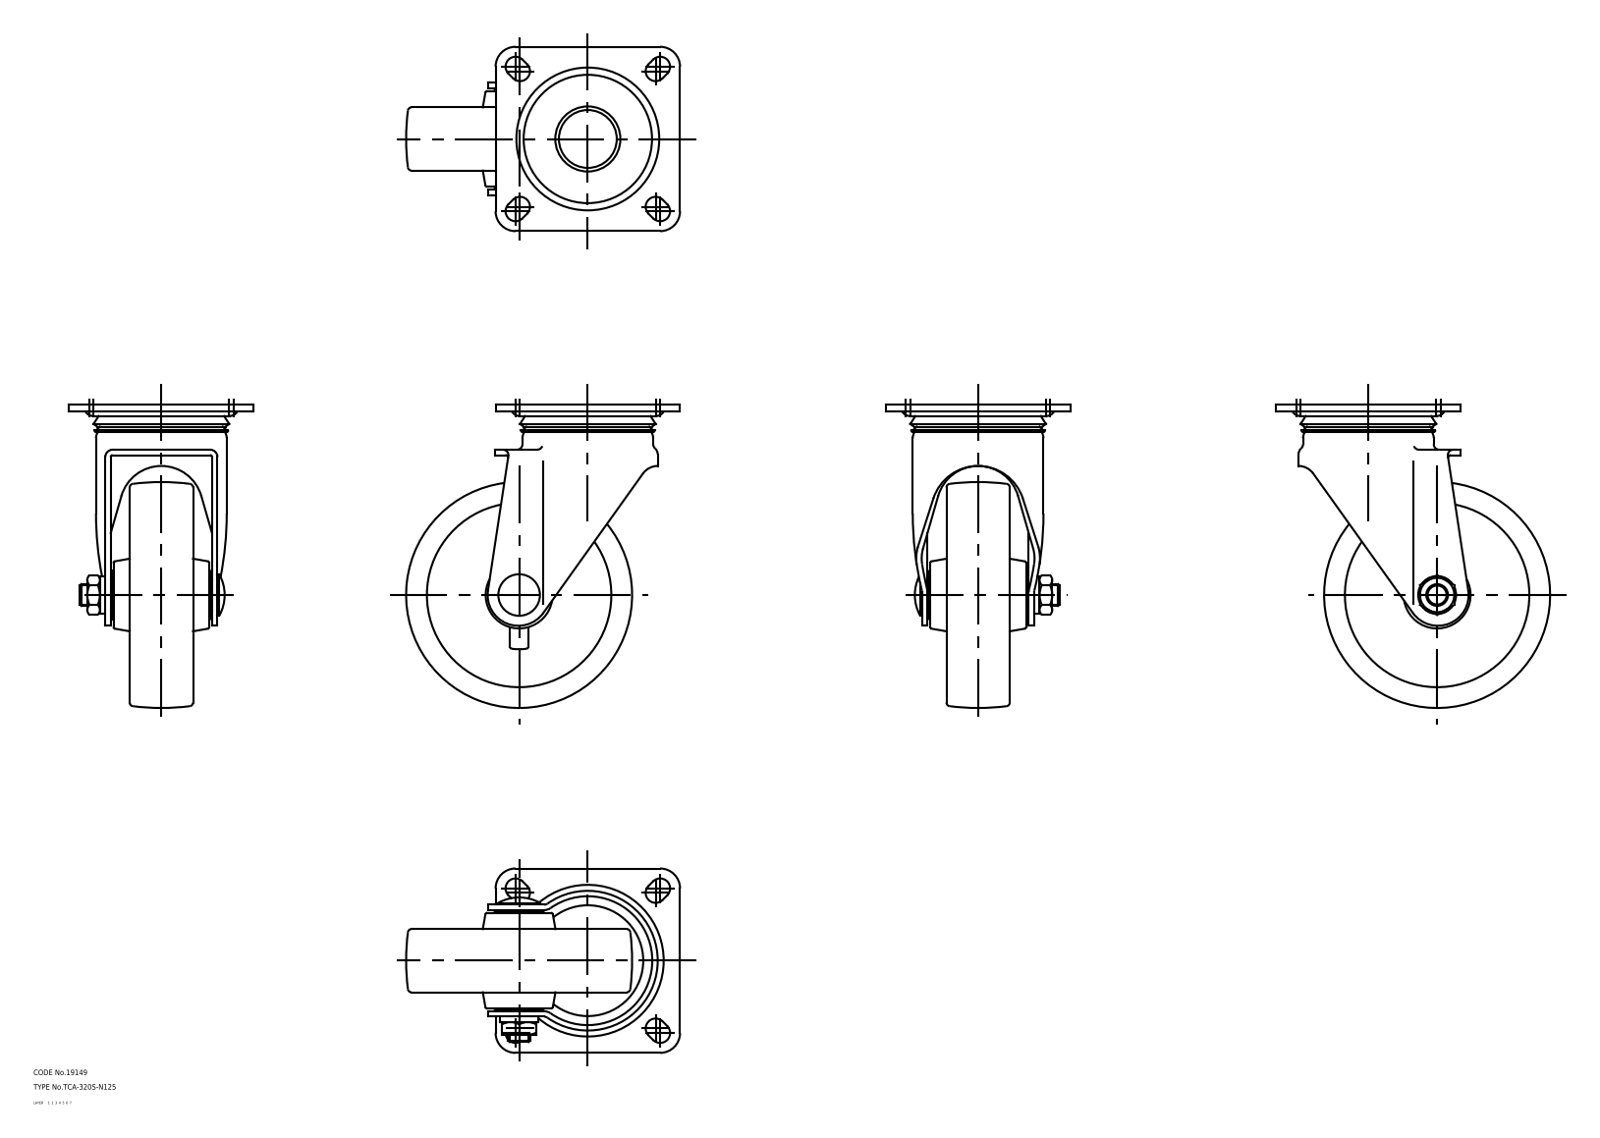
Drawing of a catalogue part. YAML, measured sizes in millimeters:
part_name: "67128369; 67128382; 67128395; 67128408 (+1 more)"
step_written_by: "CADfix (AUTOMOTIVE_DESIGN)"
units: millimeters
bodies: {solids: 5, faces: 253, planar: 0, cylindrical: 0, other: 253}
overall_size: [168, 151.5, 102]
volume: 502195
surface_area: 119551
